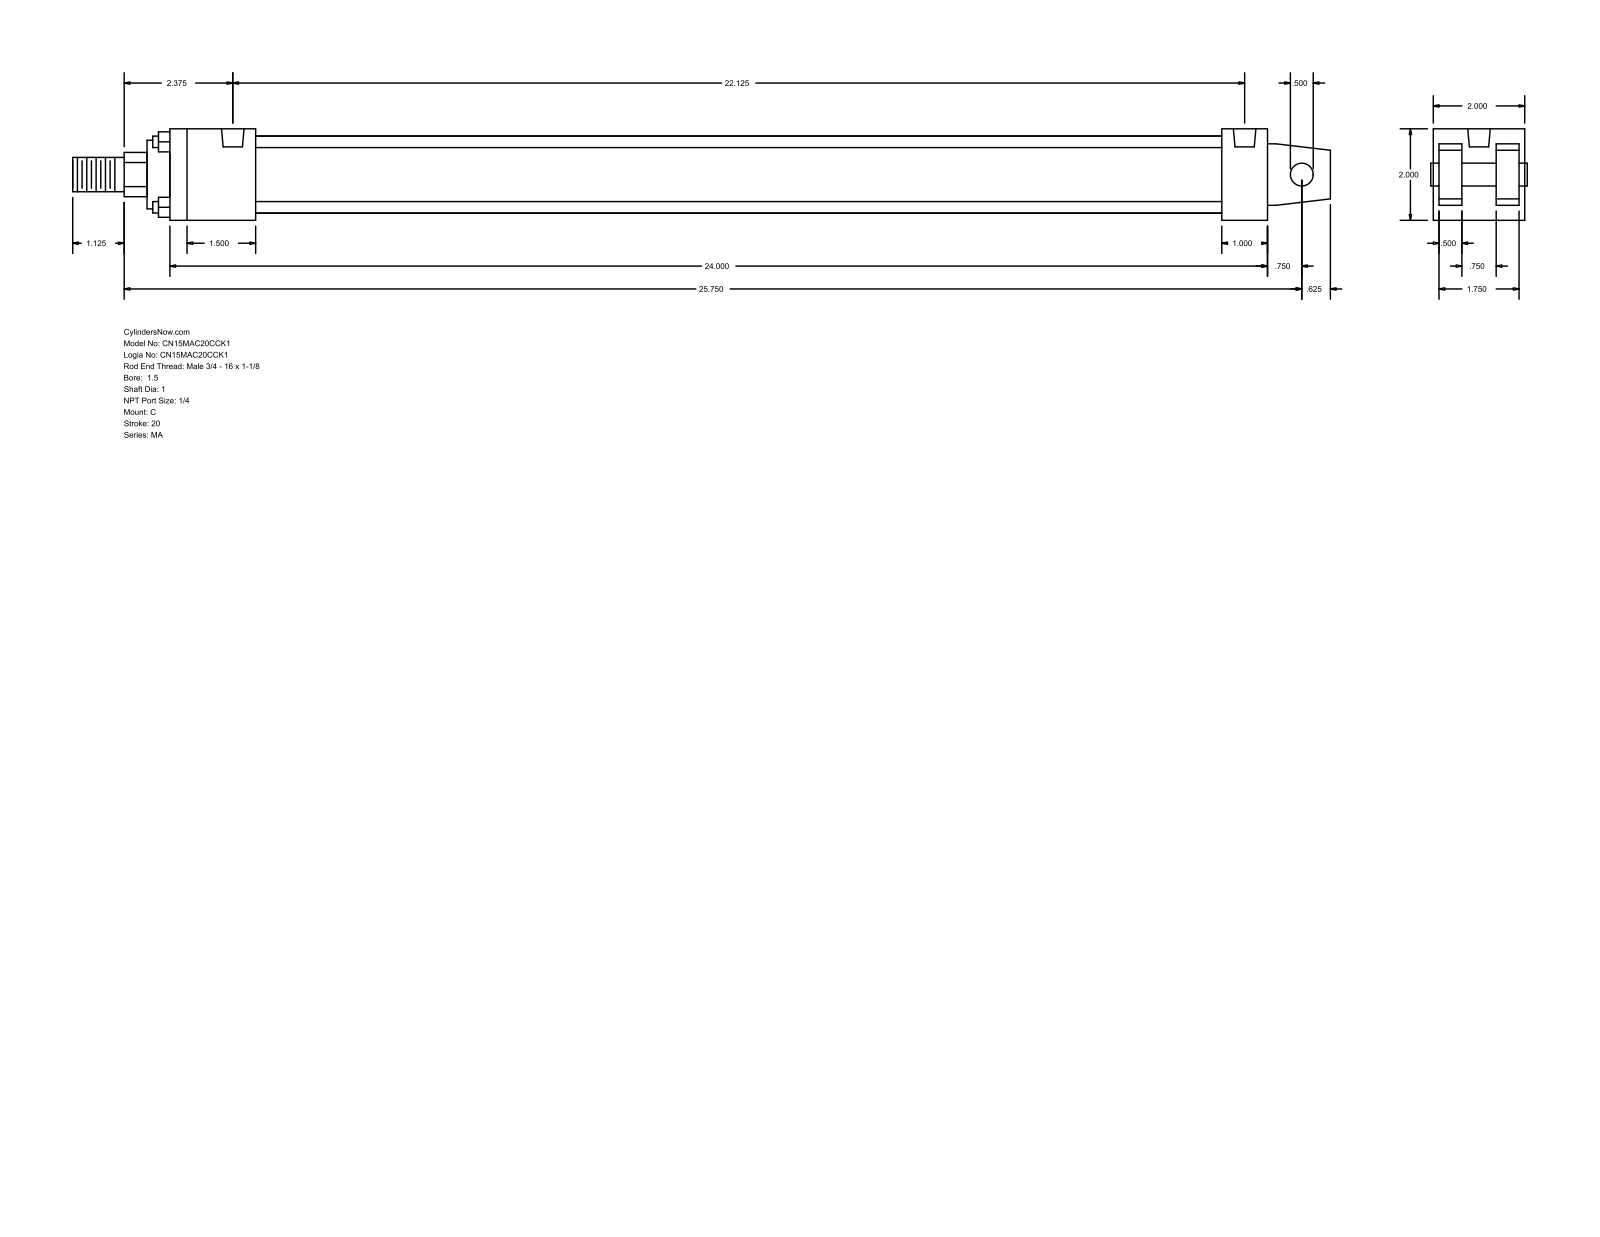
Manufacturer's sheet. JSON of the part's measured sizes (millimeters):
{"part_name": "MA_C__0150_1", "step_written_by": "GSSL Pune (CONFIG_CONTROL_DESIGN)", "units": "millimeters", "bodies": {"solids": 0, "faces": 103, "planar": 76, "cylindrical": 27, "other": 0}, "overall_size": [698.5, 50.8, 50.8], "round_holes": [[7.94, 4], [12.49, 2]], "round_bosses_or_shafts": [[6.35, 4], [42.93, 1], [38.1, 1], [25.4, 1], [19.05, 1], [12.7, 1]], "partial_cylinders_radius": [[12.29, 1]], "face_to_face_distances": [50.8, 47.63, 12.7, 3.17, 15.87, 34.93, 31.76, 609.6, 25.4, 584.2], "hole_center_spacings": [561.97]}
